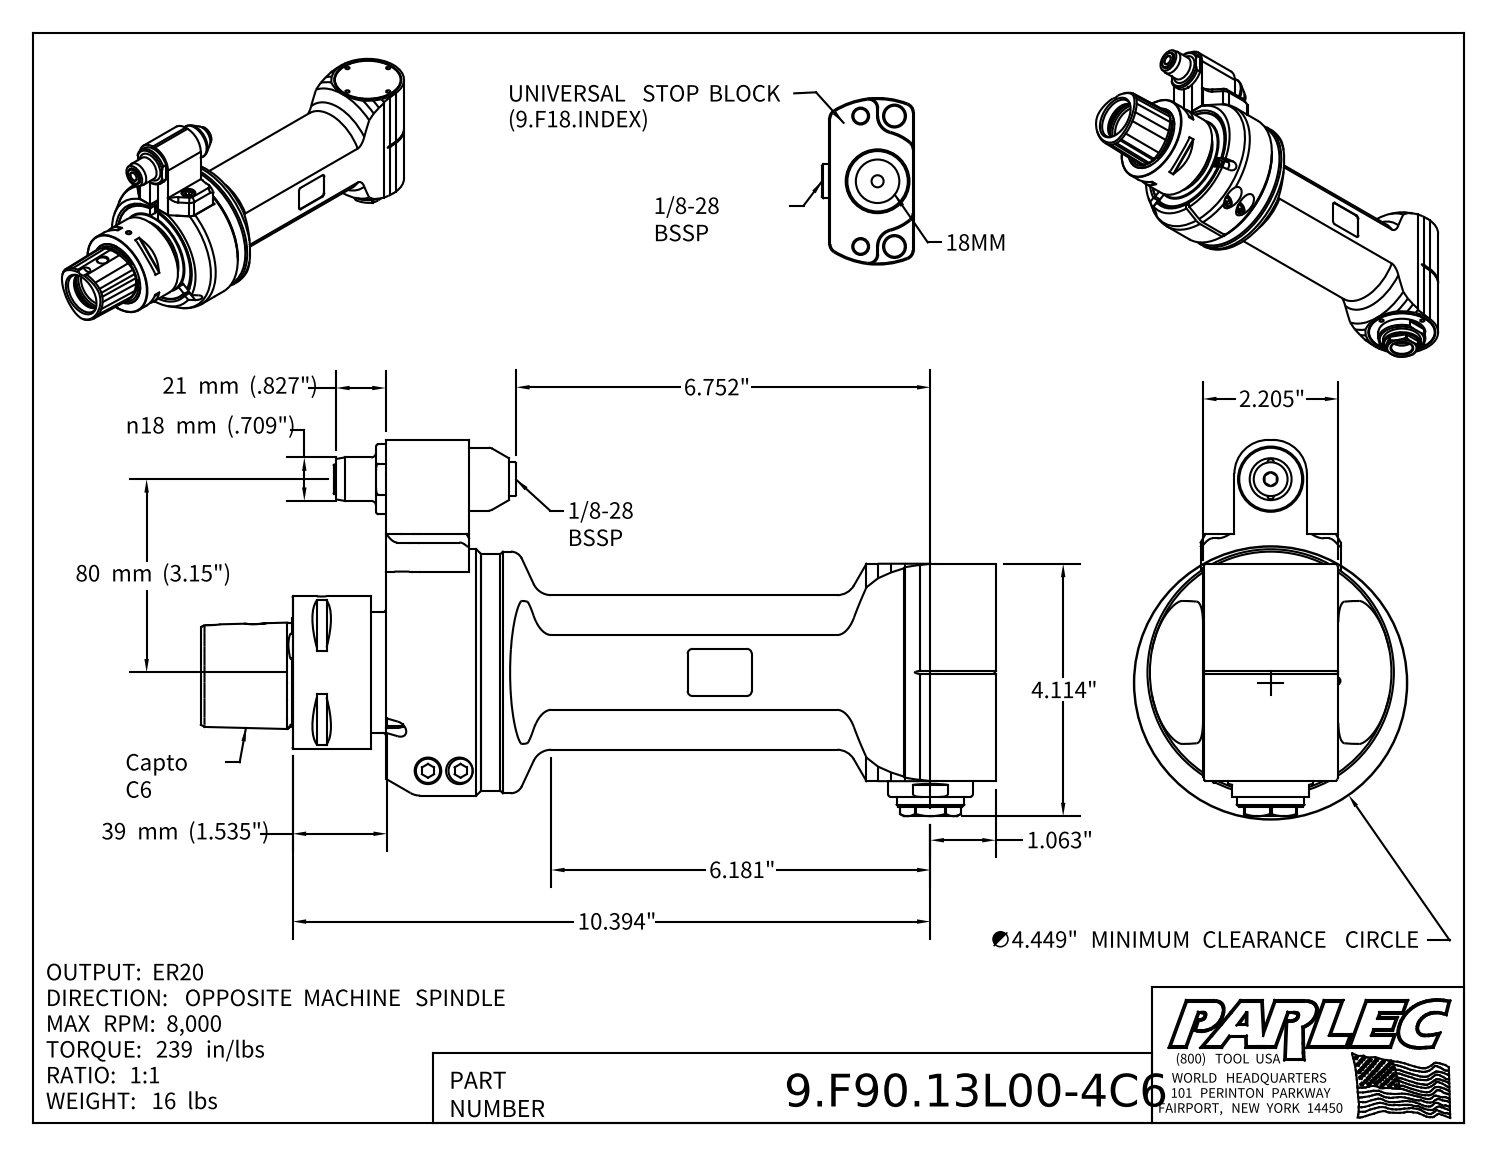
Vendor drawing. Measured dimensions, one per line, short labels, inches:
name: 9.F90.13L00-4C6; 9_F90_13L00
written by: Autodesk Inventor 2025 (AUTOMOTIVE_DESIGN)
unit: in
bodies: 5 solids, 530 faces (236 planar, 118 cylindrical, 176 other)
size: 12.953 × 6.132 × 4.016
volume: 79.66 in³; area: 250.1 in²
holes: 4× ⌀0.126, 2× ⌀0.102, 2× ⌀0.165, 2× ⌀0.197, 2× ⌀0.409, 2× ⌀0.433, 2× ⌀0.492, 1× ⌀0.098, 1× ⌀0.118, 1× ⌀0.157, 1× ⌀0.256, 1× ⌀0.276
bosses: 4× ⌀0.394, 4× ⌀0.236, 2× ⌀0.315, 2× ⌀0.098, 1× ⌀4.016, 1× ⌀3.937, 1× ⌀3.858, 1× ⌀3.031
rounds: 12× R0.079, 4× R0.157, 3× R0.197, 2× R0.016, 2× R0.02, 2× R0.039, 2× R0.138, 2× R0.551
face distances: 1.26, 2.205, 0.02, 0.512, 1.555, 1.791, 0.295, 0.531, 0.256, 0.276
hole spacings: 0.846, 1.197, 0.276, 0.848, 1.693, 9.957, 11.037, 0.049
